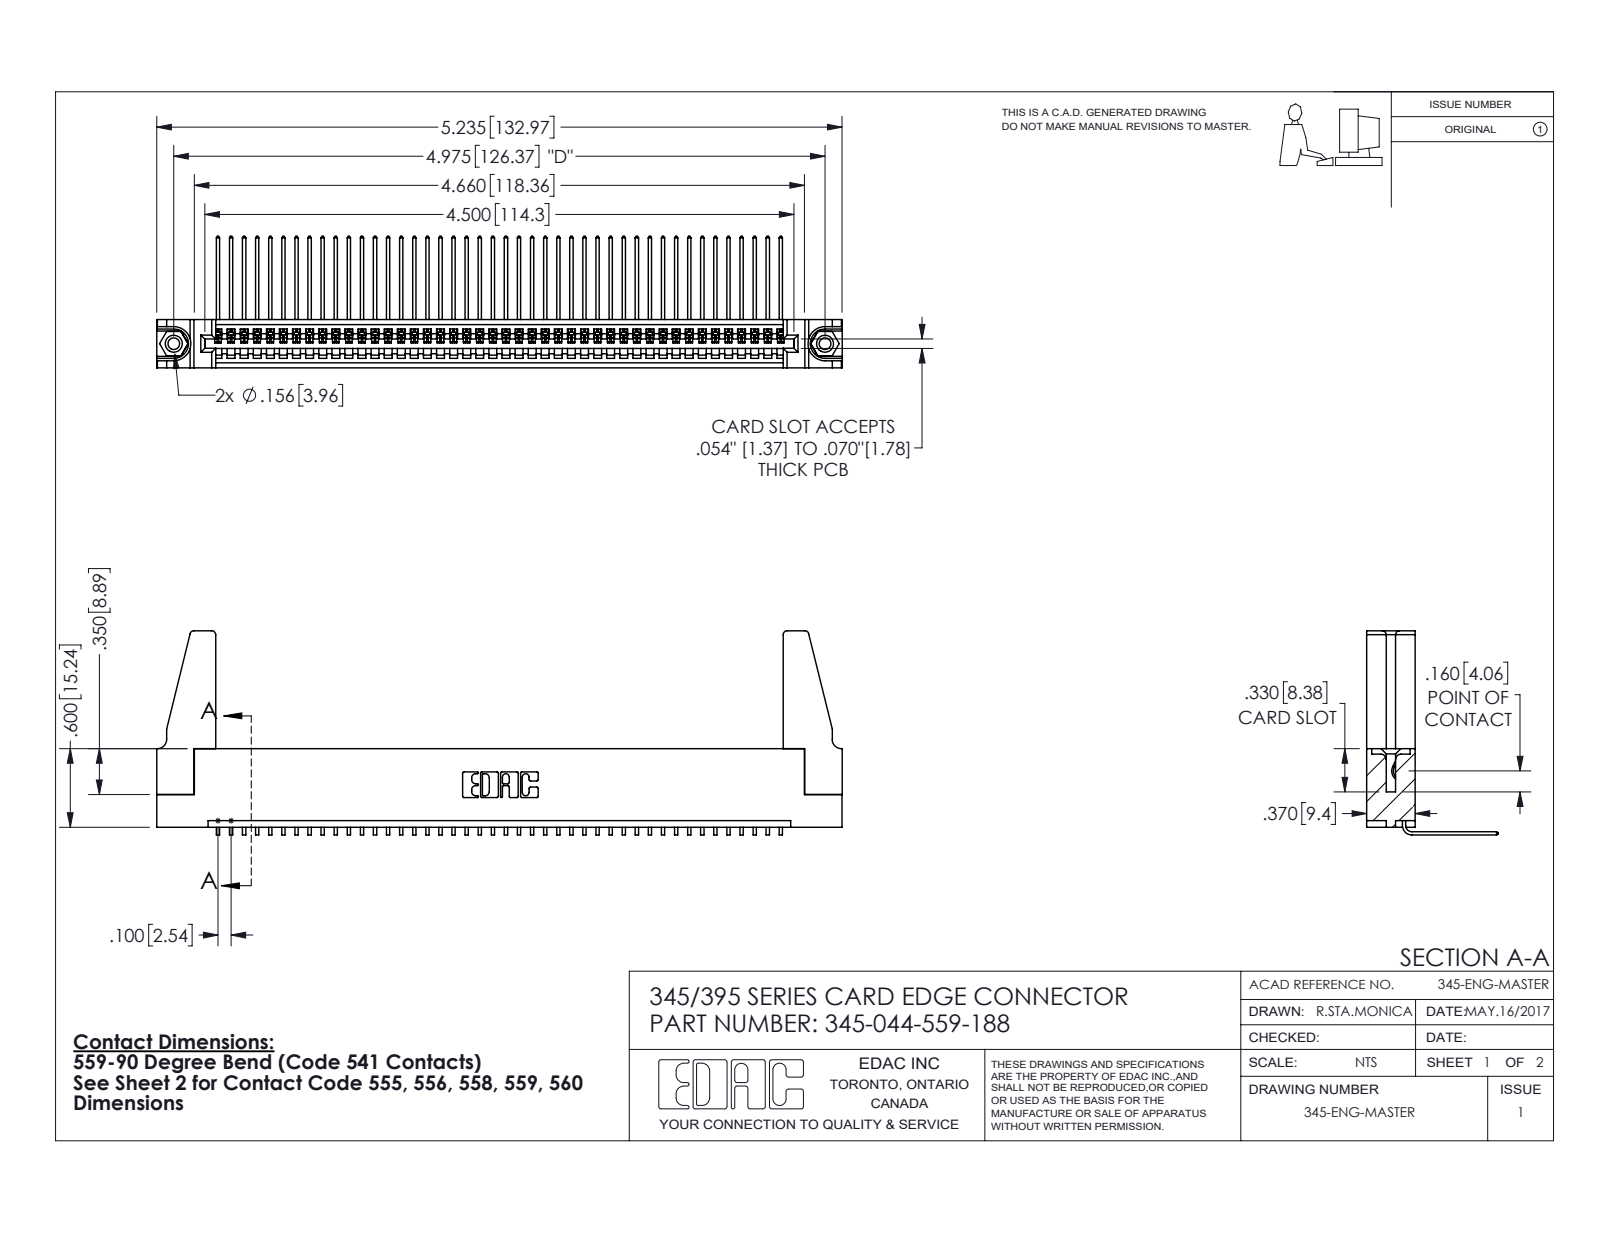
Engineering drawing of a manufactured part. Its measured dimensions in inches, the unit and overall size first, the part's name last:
Units: inches
Overall size (bounding box): 5.236 × 1.559 × 1.005
Round holes (diameter × count): ⌀0.089 ×2, ⌀0.125 ×2, ⌀0.156 ×2, ⌀0.064 ×1
Round bosses / shafts (diameter × count): ⌀0.155 ×2
Partial cylindrical surfaces — rounded edges, fillets, slot ends (radius × count): R0.006 ×88, R0.01 ×22, R0.03 ×8, R0.007 ×6, R0.031 ×6, R0.026 ×3, R0.031 ×2, R0.04 ×2
Main face-to-face distances: 0.072, 0.298, 0.37, 0.2, 0.098, 0.272, 0.025, 0.225, 0.149, 0.072
Hole centre spacings: 0.27, 4.739, 4.975
Volume: 0.979 in³ · Surface area: 32.58 in²
Bodies: 49 solids, 2890 faces (2000 planar, 874 cylindrical, 16 other)
Part name (STEP PRODUCT): 345-220-078_345-220-088; 345-292-001_558 559 Tail - 1; 345-250-001_345-250-001-102; 345 Part_Flush Mounting Lugs - 0.156 Dia-TH (+1 more)
STEP written by: SolidWorks 2016 (CONFIG_CONTROL_DESIGN)
